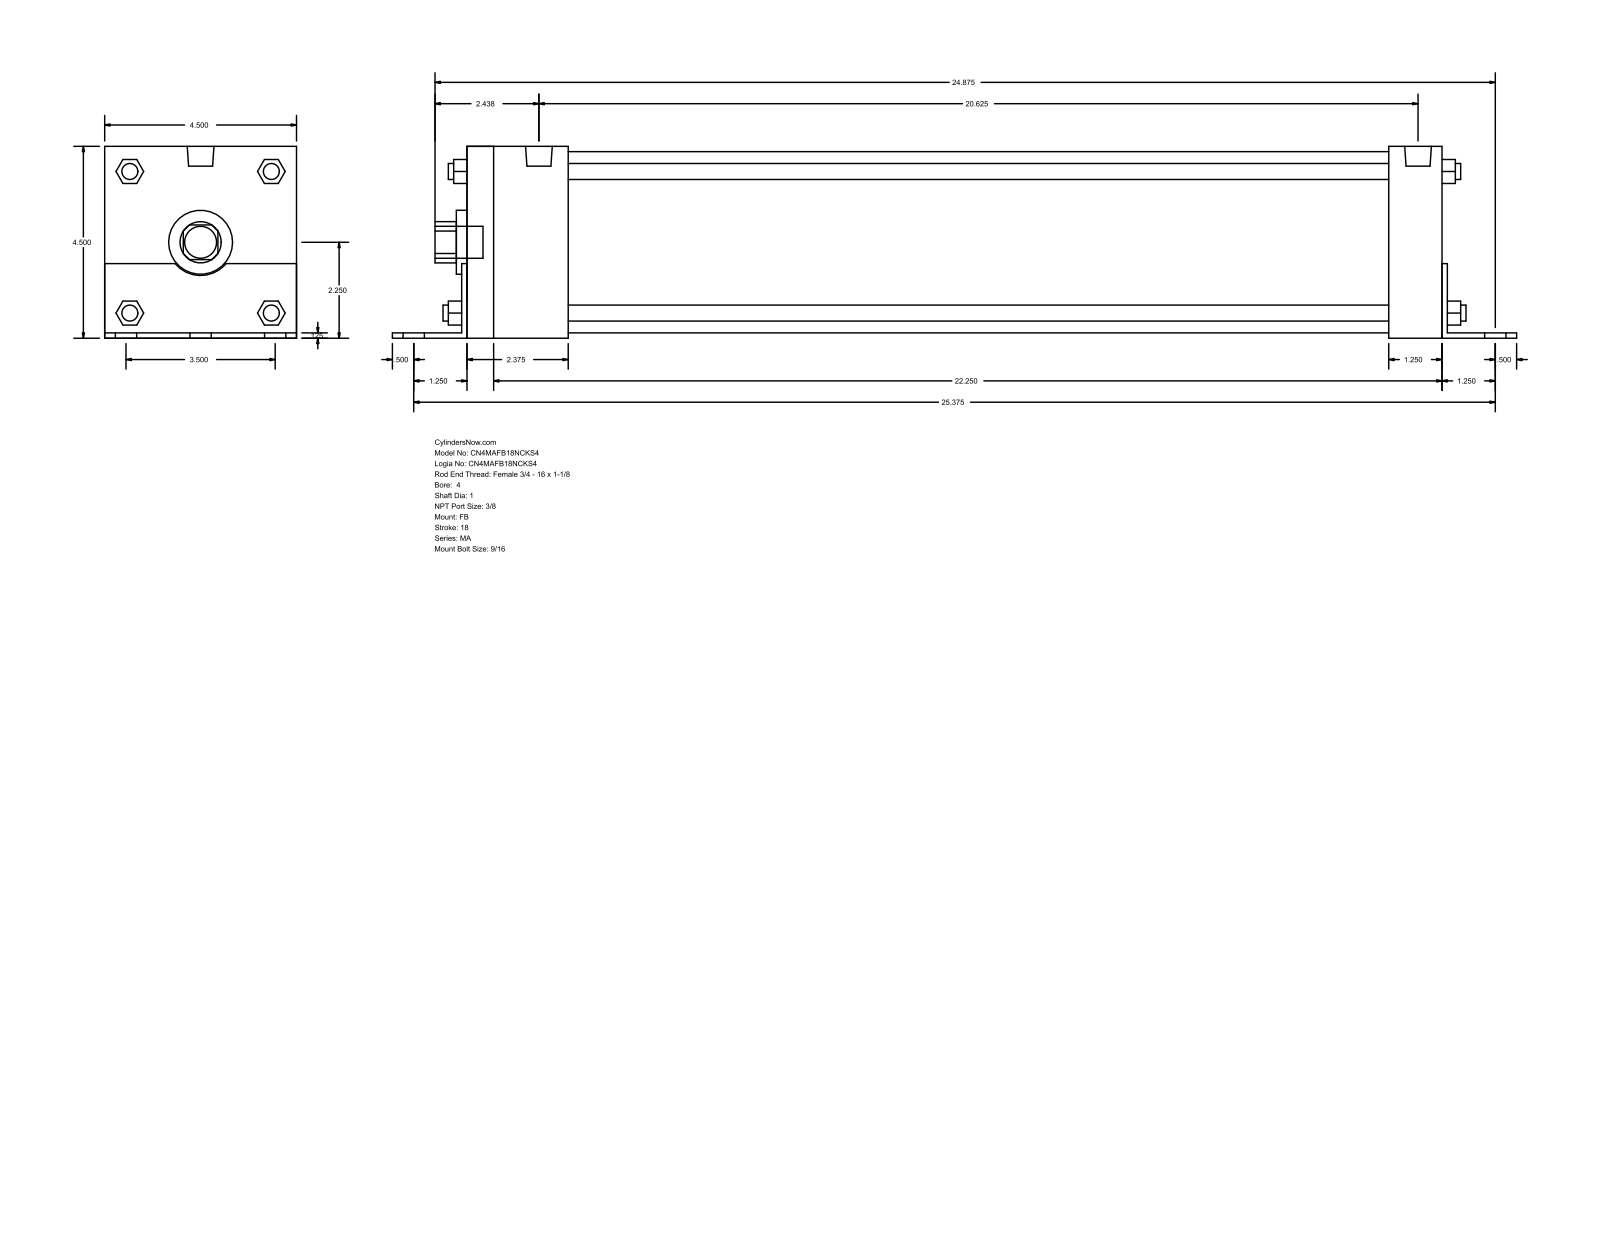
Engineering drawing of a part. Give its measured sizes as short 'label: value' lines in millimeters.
name: MA_FB__0400_1
written by: GSSL Pune (CONFIG_CONTROL_DESIGN)
unit: mm
bodies: 0 solids, 140 faces (105 planar, 35 cylindrical, 0 other)
size: 669.92 × 114.35 × 114.3
holes: 1× ⌀25.4, 1× ⌀38.1, 1× ⌀107.95
bosses: 6× ⌀14.29, 4× ⌀11.11, 4× ⌀9.53, 2× ⌀15.93, 1× ⌀19.05
rounds: 1× R12.29, 1× R19.81
face distances: 114.3, 3.17, 114.35, 584.2, 3.12, 111.18, 581.03, 587.37, 552.45, 549.28
